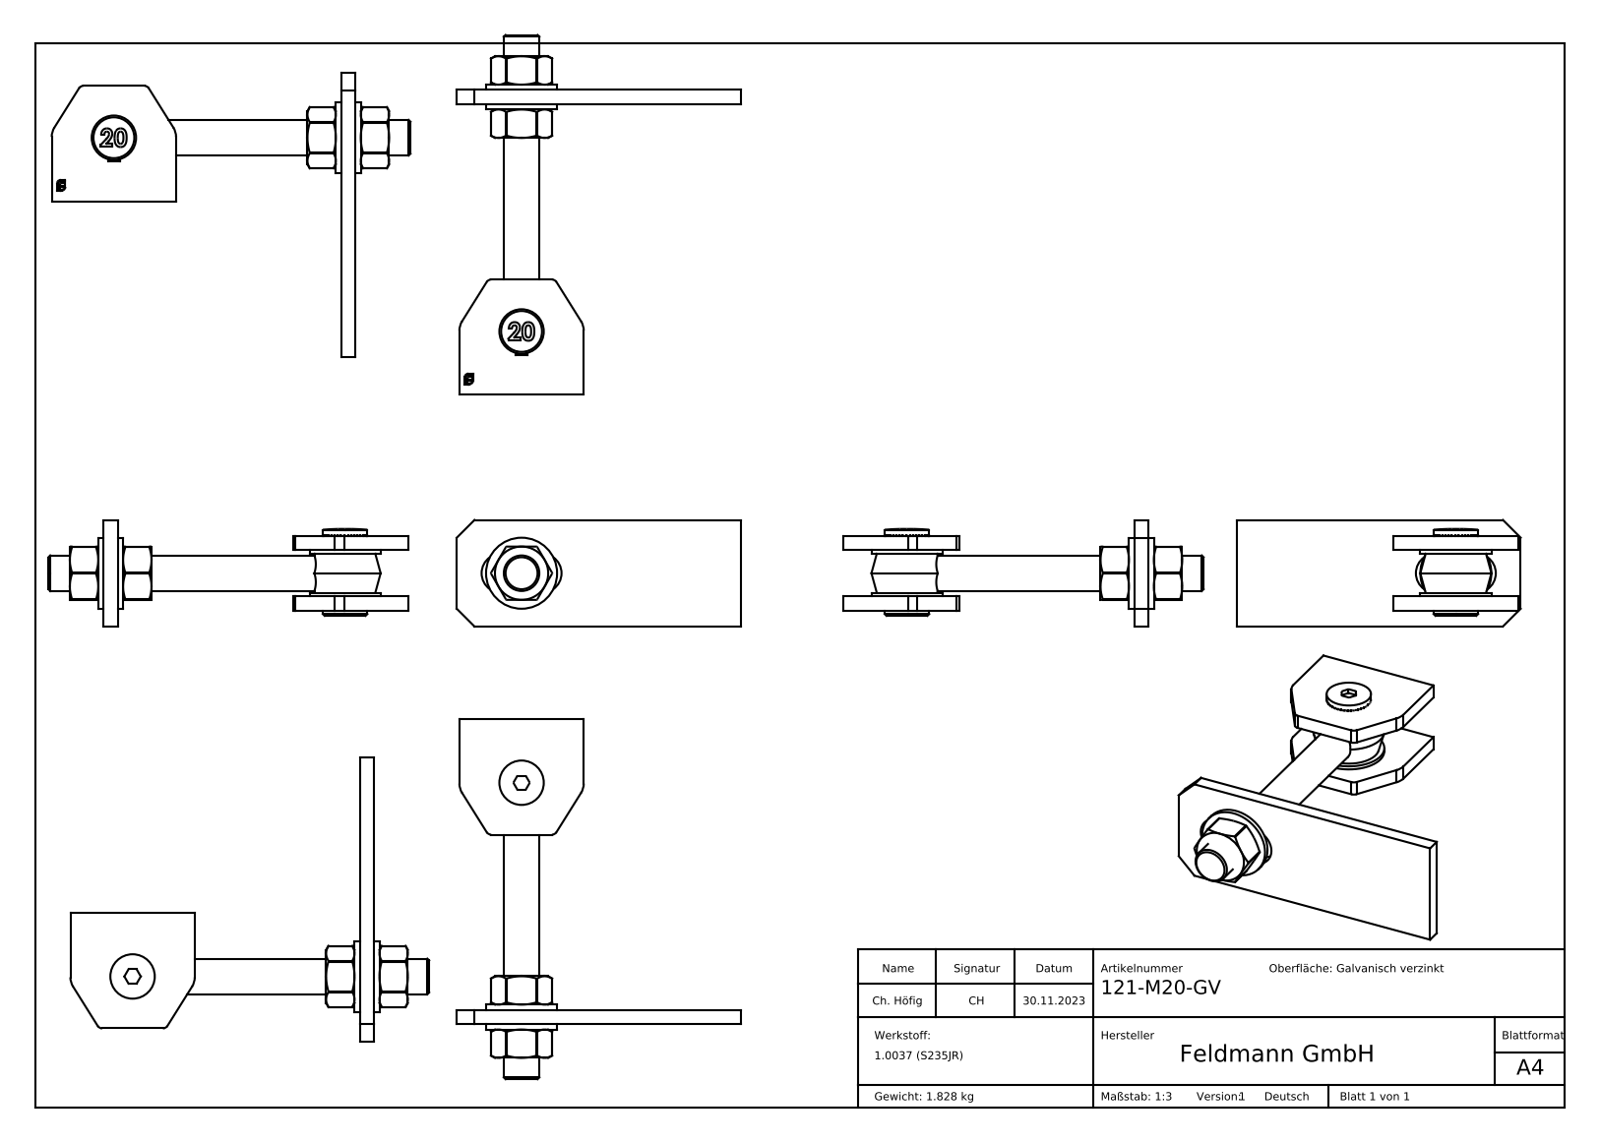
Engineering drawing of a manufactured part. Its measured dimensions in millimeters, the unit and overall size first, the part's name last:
Units: millimetres
Overall size (bounding box): 202.75 × 160 × 60
Round holes (diameter × count): ⌀8.5 ×1, ⌀16.4 ×1, ⌀16.5 ×1, ⌀17.5 ×1, ⌀21 ×1
Round bosses / shafts (diameter × count): ⌀40 ×2, ⌀25 ×1, ⌀20 ×1, ⌀15.7 ×1, ⌀10 ×1
Partial cylindrical surfaces — rounded edges, fillets, slot ends (radius × count): R0.5 ×6, R3 ×2, R10 ×2, R11 ×2
Main face-to-face distances: 8, 34, 26, 2, 42, 24, 32, 10, 19, 3
Volume: 233 975 mm³ · Surface area: 79 405 mm²
Bodies: 12 solids, 592 faces (380 planar, 41 cylindrical, 171 other)
Part name (STEP PRODUCT): DIN 934 M4-M20_DIN 934 M20; 121-Mxx Teil6_121-M20-GV Teil6; Torband Teil3_121-M20-GV Teil3; 121-M20-GV (+6 more)
STEP written by: SolidWorks 2018 (CONFIG_CONTROL_DESIGN)
